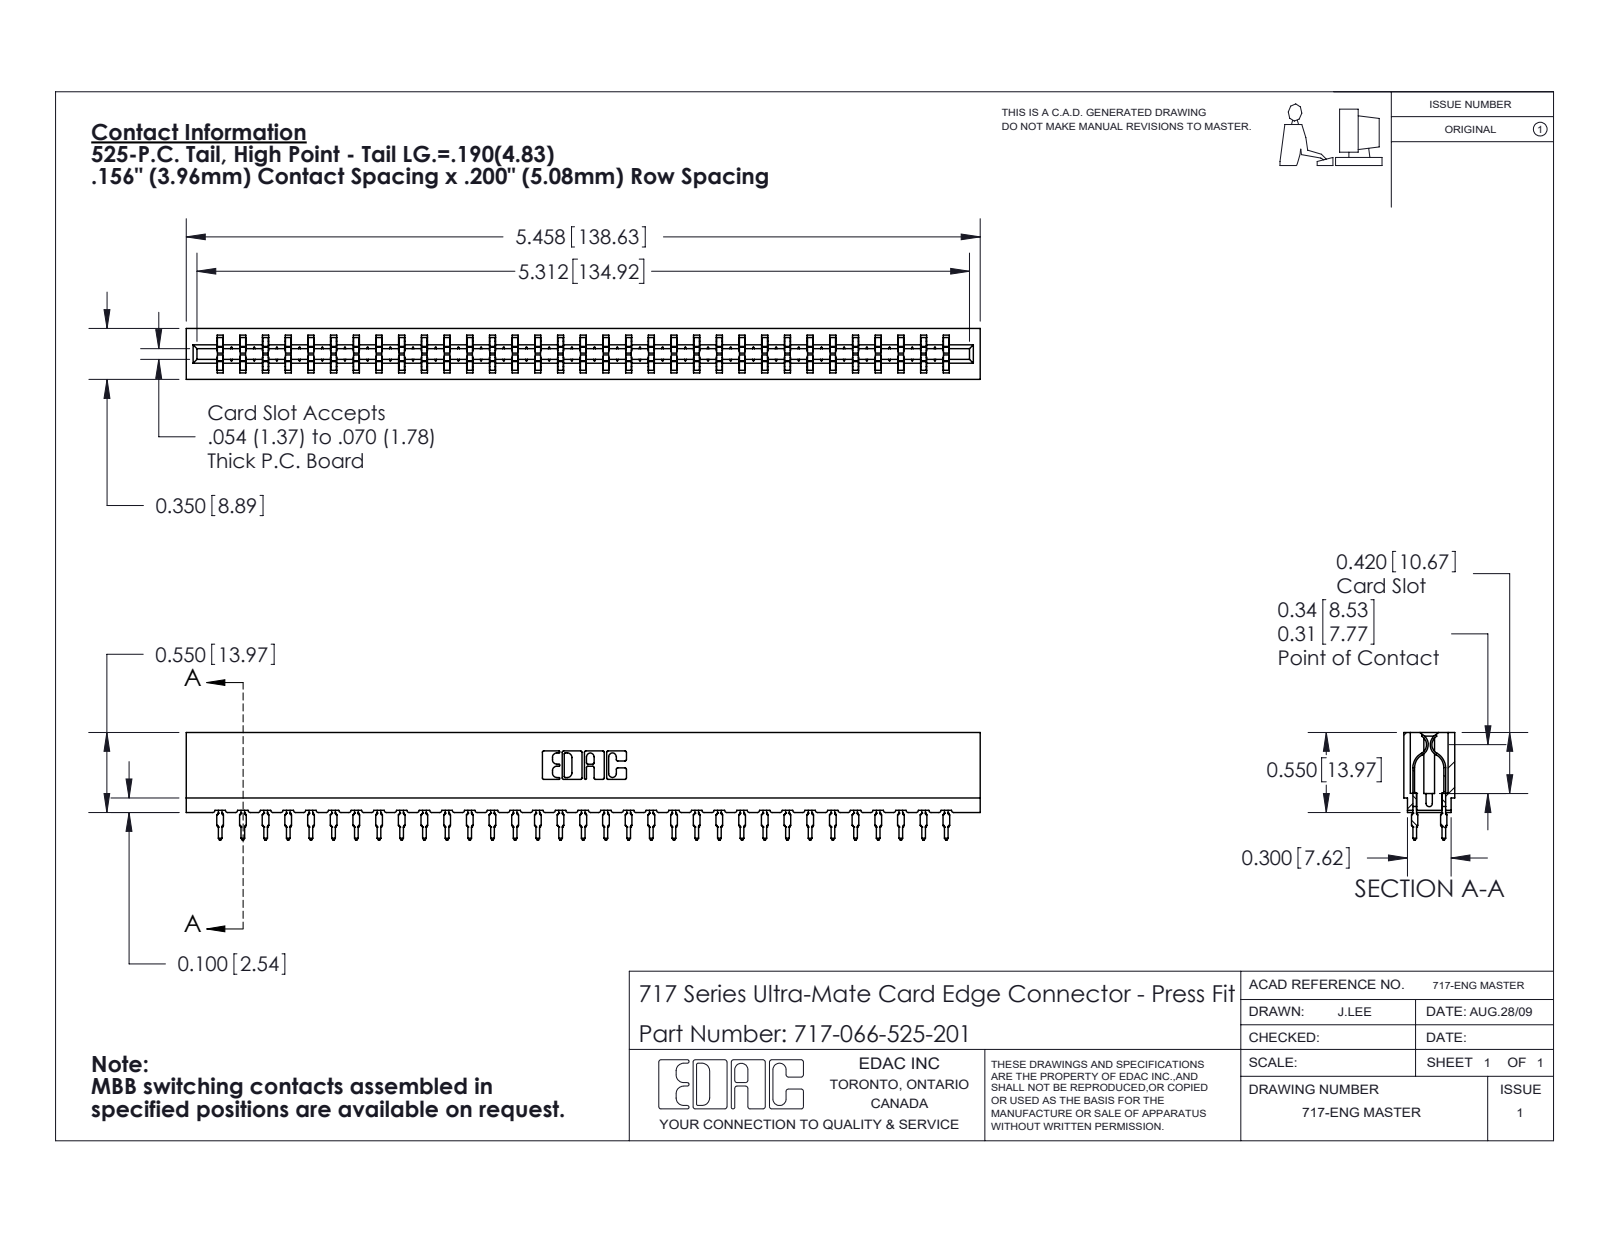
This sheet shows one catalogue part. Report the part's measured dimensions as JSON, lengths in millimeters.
{"part_name": "745-292-001_525; 717-066-525-201; 717 Part_Insulator Option - 06", "step_written_by": "SolidWorks 2020 (CONFIG_CONTROL_DESIGN)", "units": "millimeters", "bodies": {"solids": 67, "faces": 6034, "planar": 3123, "cylindrical": 1195, "other": 1716}, "overall_size": [138.6, 18.8, 8.9], "volume_mm3": 12000, "surface_area_mm2": 18210, "partial_cylinders_radius": [[0.5, 132], [0.4, 66], [0.3, 22], [0.1, 8], [0.3, 8], [0.2, 6], [0.8, 6], [0.7, 3]], "face_to_face_distances": [5.4, 3.5, 8.9, 1.6, 7.3, 1.9, 3.8, 1.9, 1.1, 7.7]}
